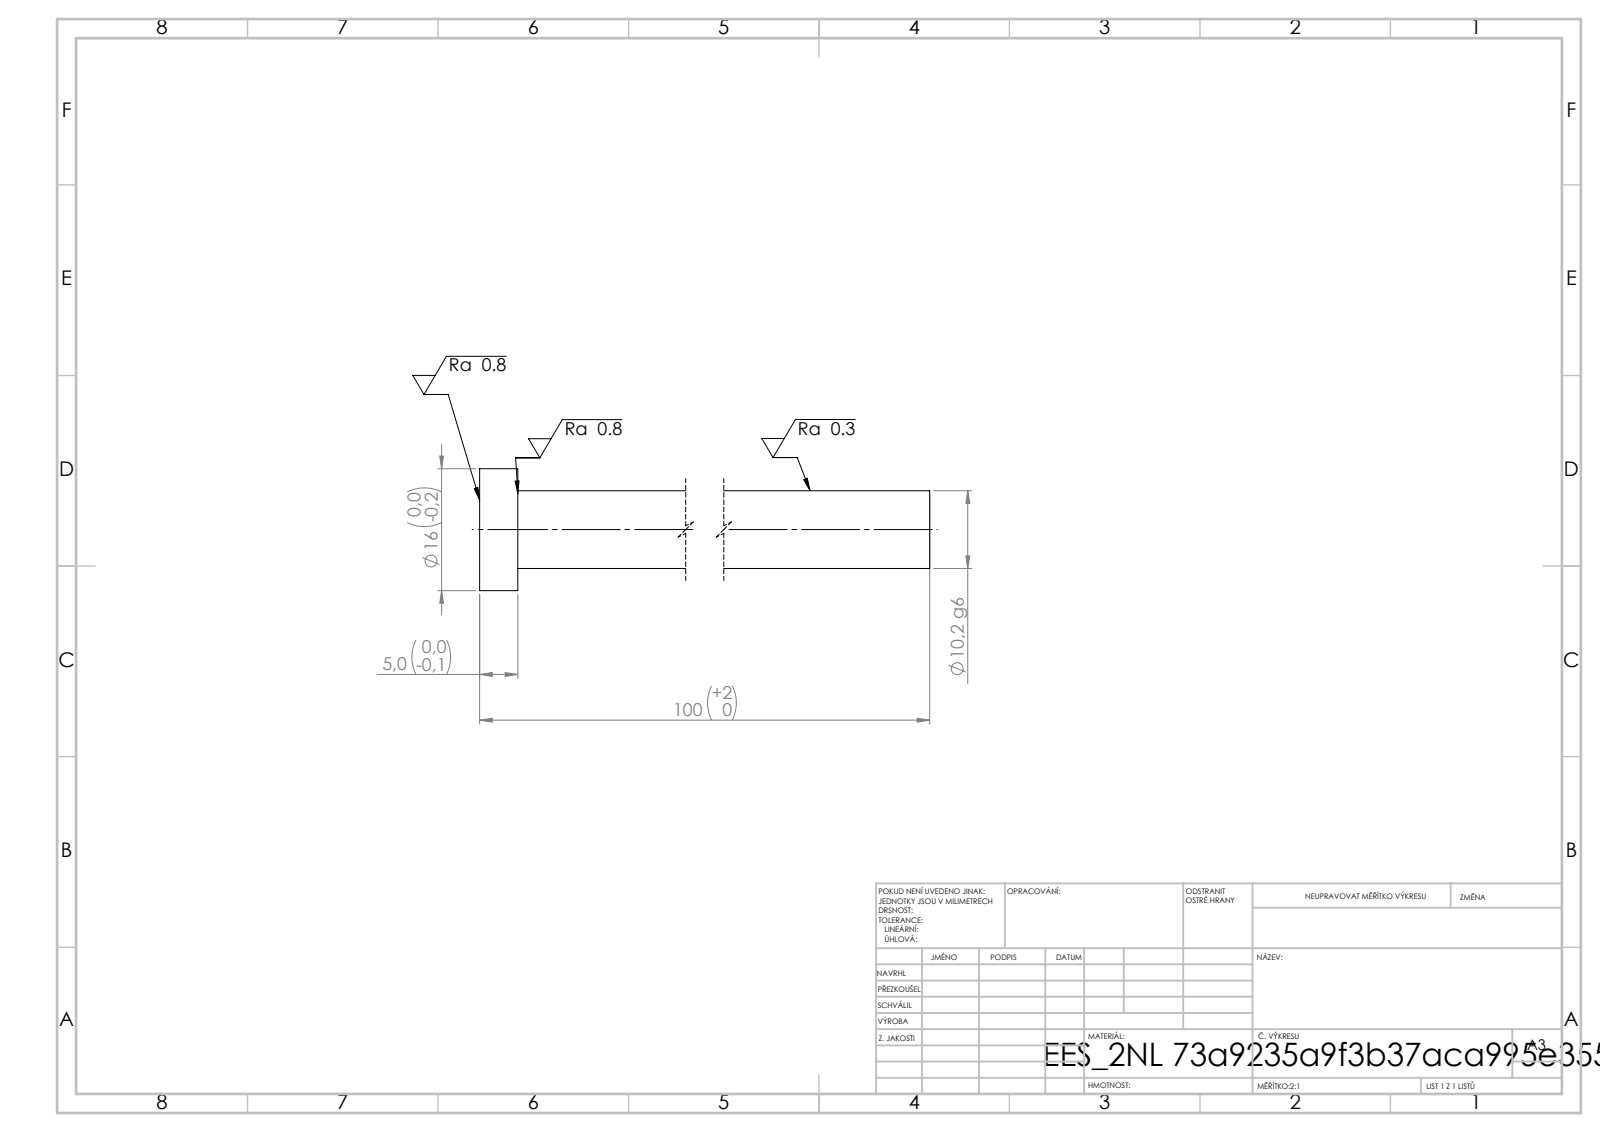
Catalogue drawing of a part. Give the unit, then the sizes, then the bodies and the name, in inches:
Units: inches
Overall size (bounding box): 3.937 × 0.63 × 0.63
Round bosses / shafts (diameter × count): ⌀0.63 ×1, ⌀0.402 ×1
Main face-to-face distances: 0.197, 3.937, 3.74
Volume: 0.535 in³ · Surface area: 5.732 in²
Bodies: 1 solid, 7 faces (3 planar, 4 cylindrical, 0 other)
STEP written by: SolidWorks 2019 (CONFIG_CONTROL_DESIGN)
